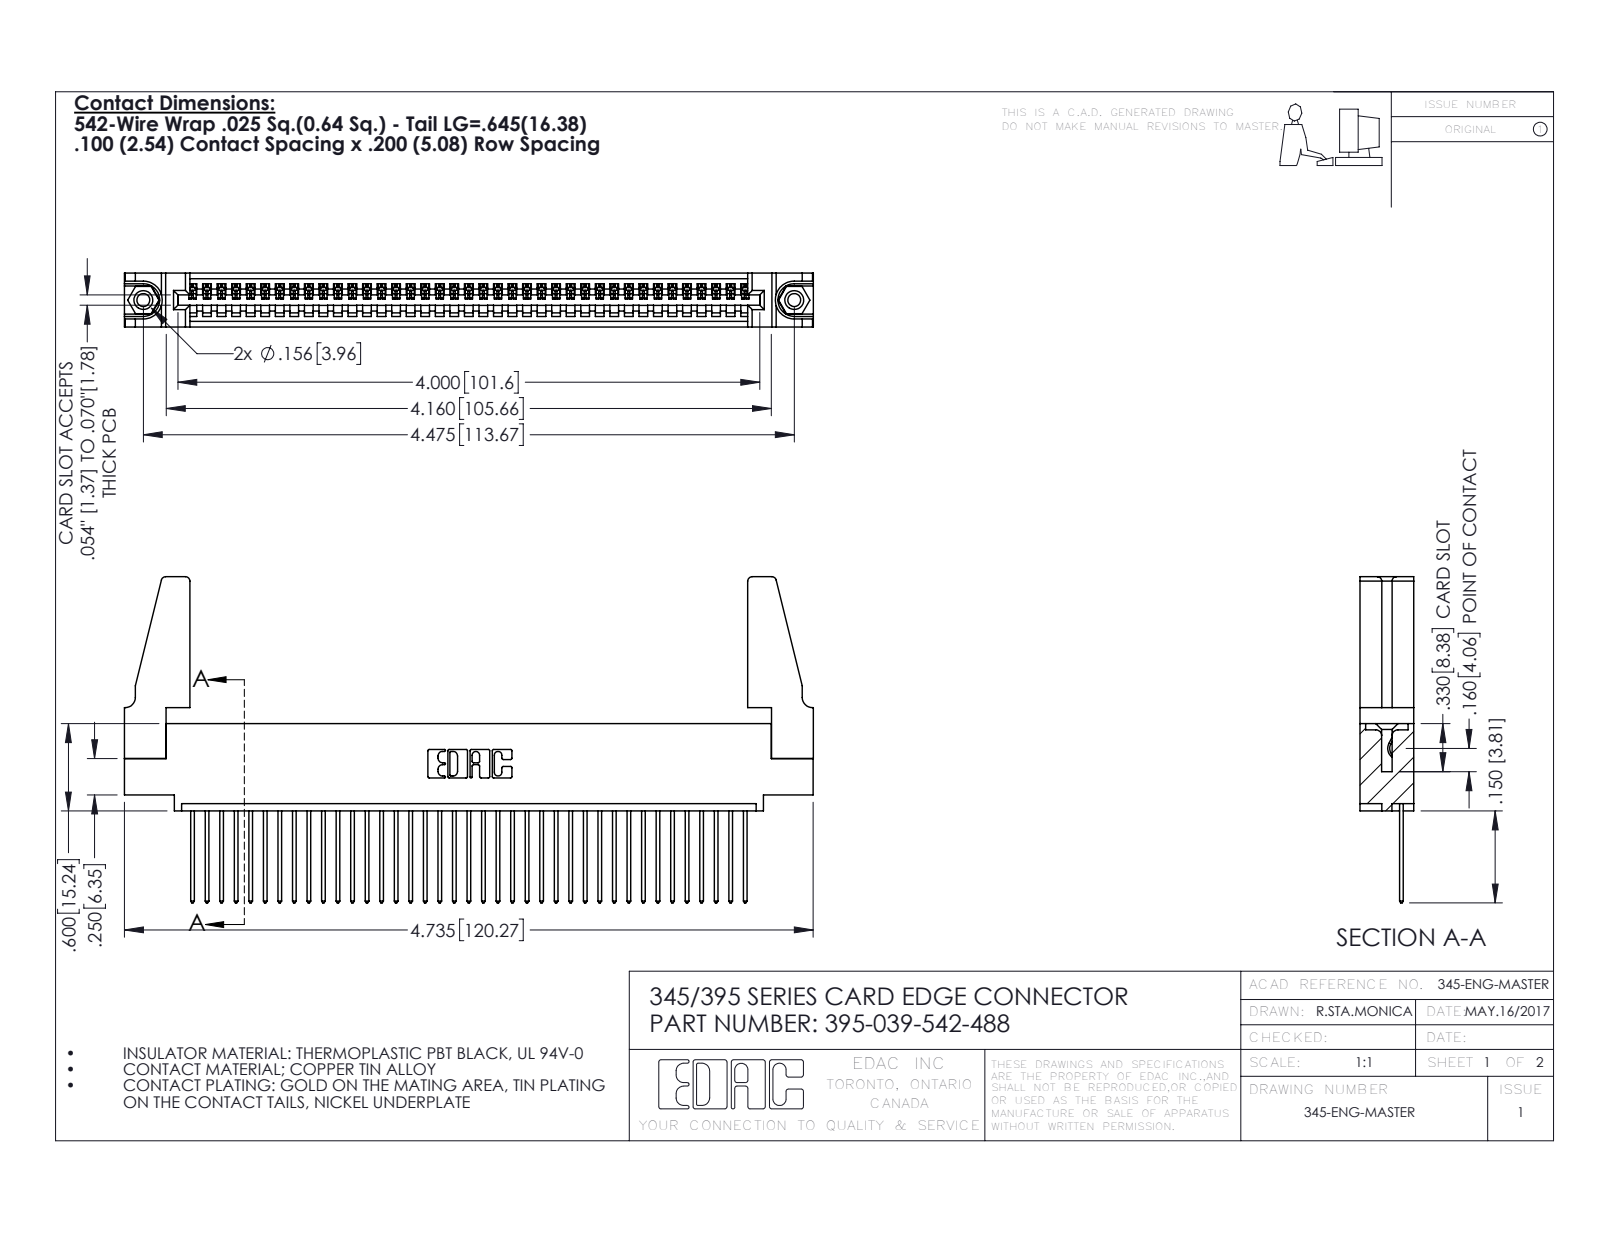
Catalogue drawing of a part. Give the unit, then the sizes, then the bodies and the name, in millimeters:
Units: millimetres
Overall size (bounding box): 120.3 × 56.9 × 9.4
Round holes (diameter × count): ⌀2.3 ×2, ⌀3.2 ×2, ⌀4 ×2, ⌀1.6 ×1
Round bosses / shafts (diameter × count): ⌀3.9 ×2
Partial cylindrical surfaces — rounded edges, fillets, slot ends (radius × count): R0.2 ×78, R0.3 ×78, R0.3 ×22, R0.8 ×8, R0.2 ×6, R0.8 ×6, R0.7 ×3, R0.8 ×2
Main face-to-face distances: 1.8, 7.6, 9.4, 2.5, 6.9, 0.6, 5.1, 5.7, 3.8, 1.8
Hole centre spacings: 6.9, 107.7, 113.7
Volume: 14 700 mm³ · Surface area: 18 890 mm²
Bodies: 44 solids, 2516 faces (1716 planar, 784 cylindrical, 16 other)
Part name (STEP PRODUCT): 345 Part_0.110 Offset - 0.156 Dia-TH; 345-250-001_345-250-001-102; 345-292-001_345-293-142; 345-220-078_345-220-088 (+1 more)
STEP written by: SolidWorks 2016 (CONFIG_CONTROL_DESIGN)
